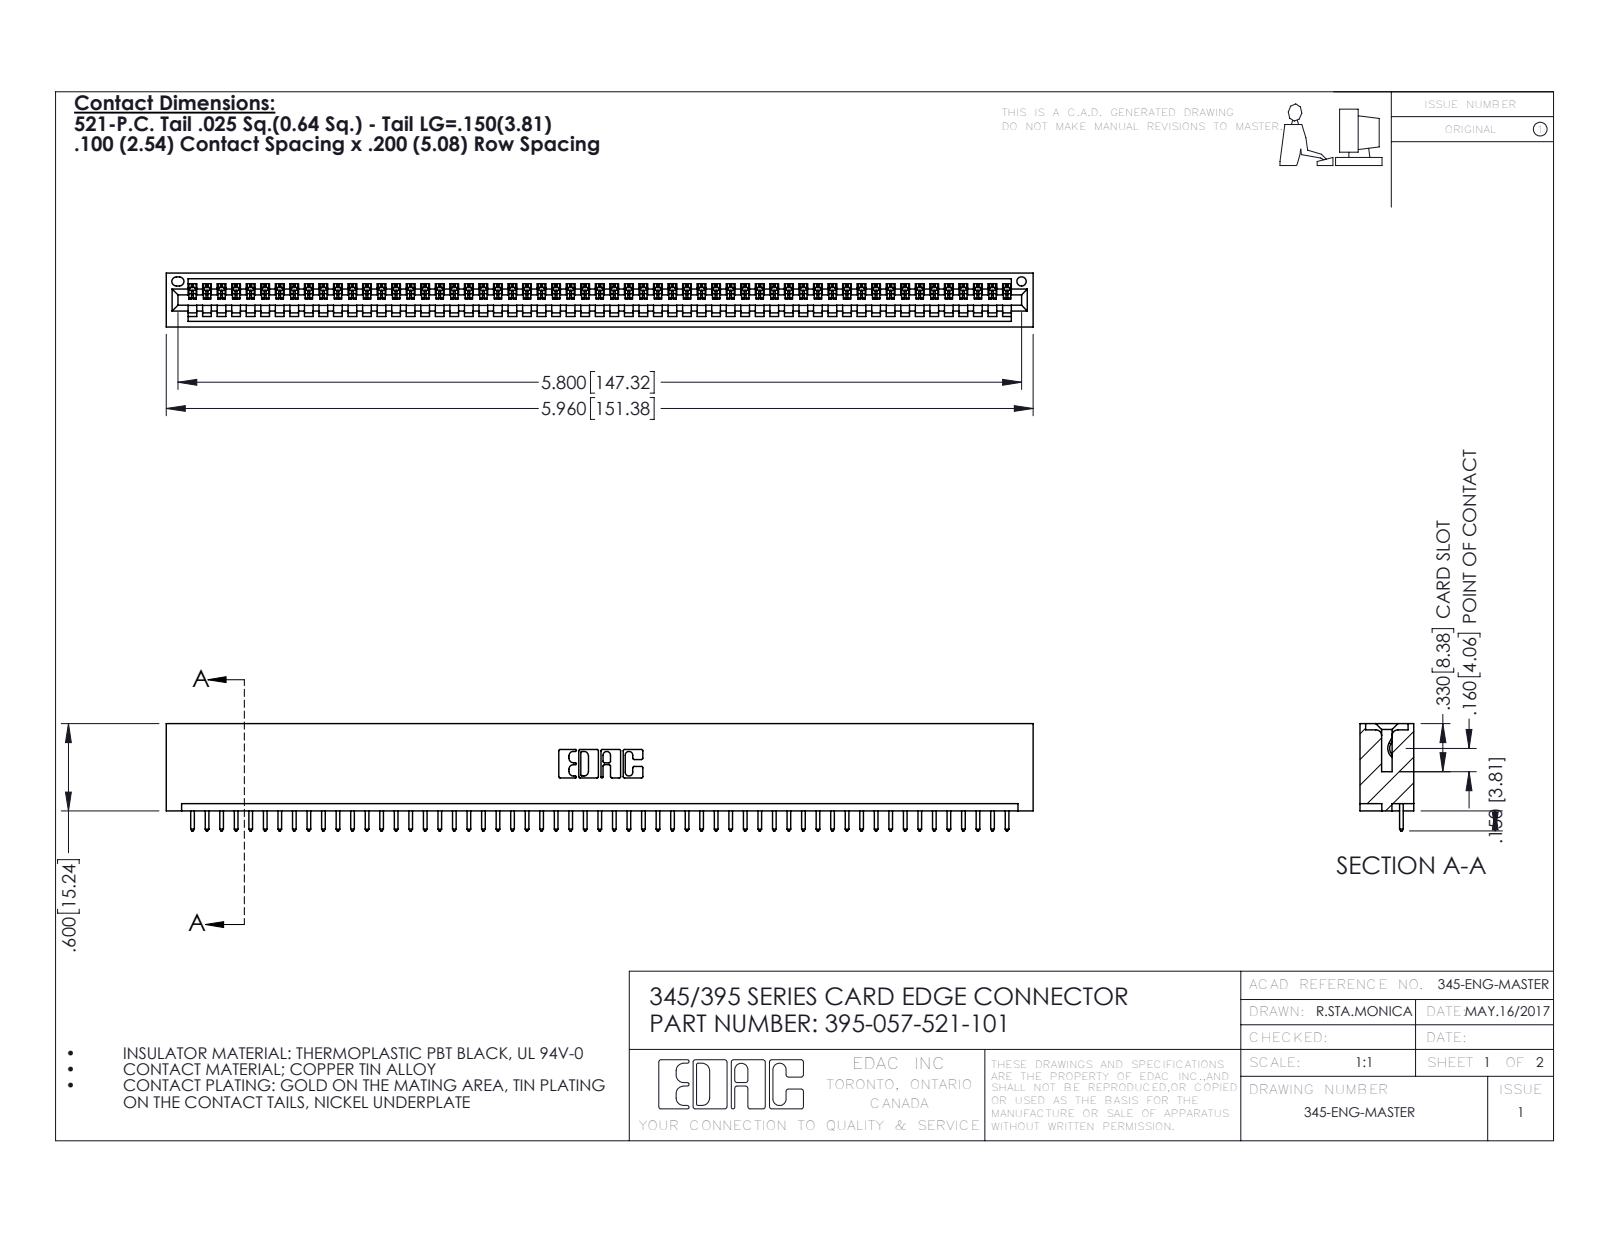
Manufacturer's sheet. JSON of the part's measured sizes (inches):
{"part_name": "345-292-001_345-293-121; 395-057-521-101; 345 Part_No Mounting Lugs", "step_written_by": "SolidWorks 2016 (CONFIG_CONTROL_DESIGN)", "units": "inches", "bodies": {"solids": 58, "faces": 3424, "planar": 2356, "cylindrical": 1068, "other": 0}, "overall_size": [5.96, 0.737, 0.37], "volume_in3": 0.911, "surface_area_in2": 30.37, "round_holes": [[0.064, 1]], "partial_cylinders_radius": [[0.006, 114], [0.01, 114], [0.01, 22], [0.007, 6], [0.031, 6], [0.026, 3], [0.031, 2], [0.04, 2]], "face_to_face_distances": [0.298, 0.072, 0.37, 0.2, 0.098, 0.272, 0.025, 0.225, 0.149, 0.072]}
